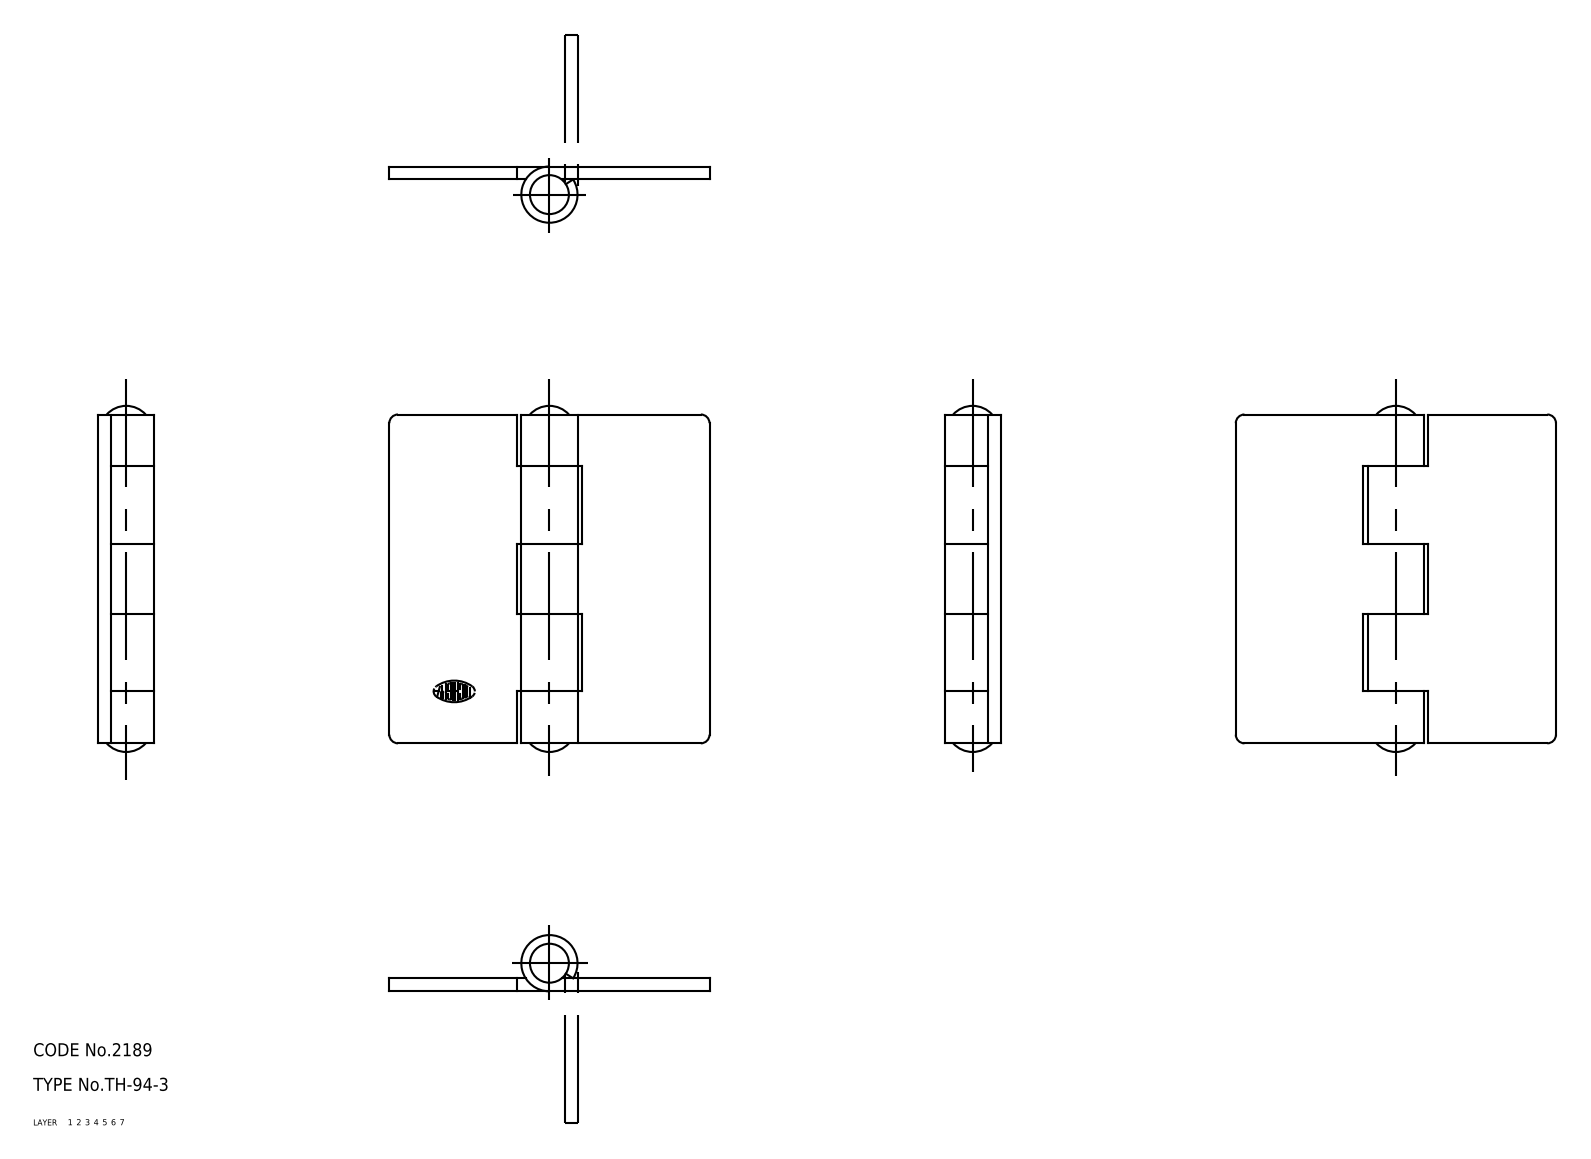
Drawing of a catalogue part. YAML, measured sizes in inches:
part_name: "hinge piece_B; hinge piece_A; shaft; TH_94_3_18963_36"
step_written_by: "CADfix (AUTOMOTIVE_DESIGN)"
units: inches
bodies: {solids: 3, faces: 48, planar: 0, cylindrical: 0, other: 48}
overall_size: [3.149, 2.913, 0.512]
volume: 1.478
surface_area: 28.3
